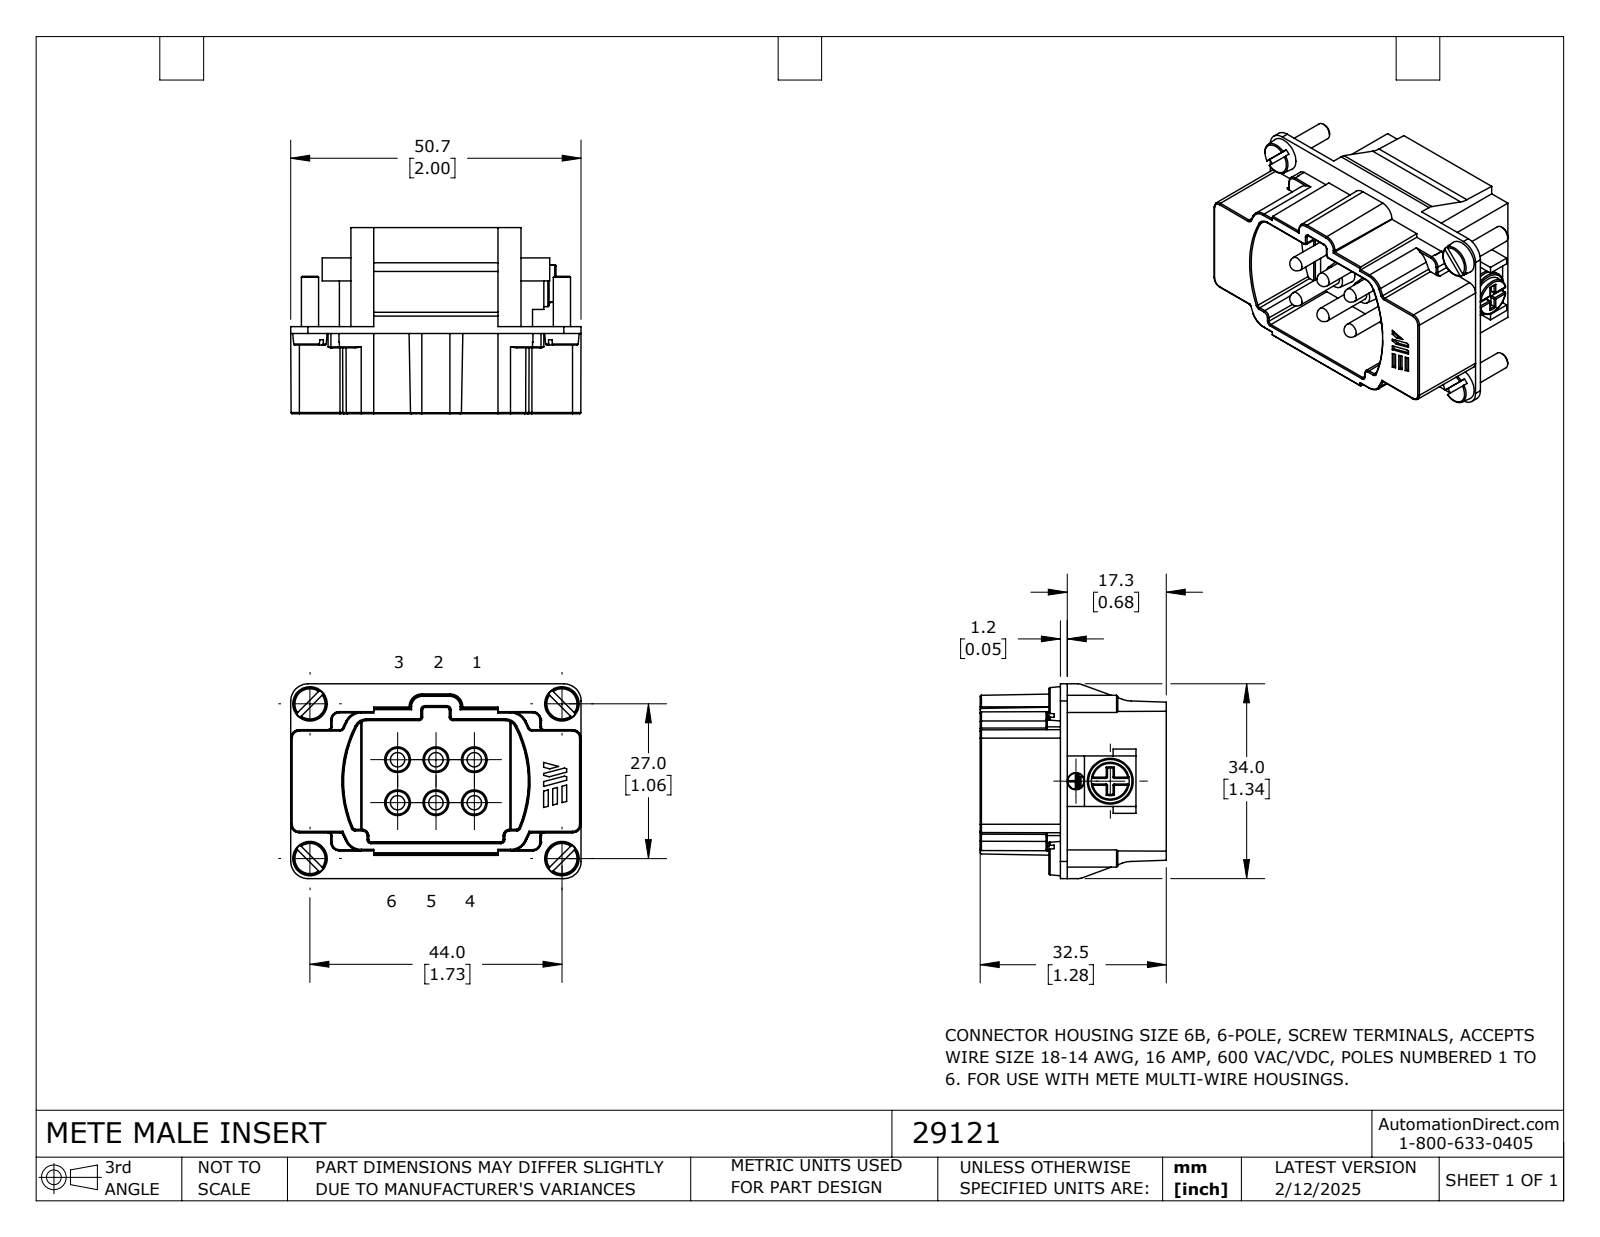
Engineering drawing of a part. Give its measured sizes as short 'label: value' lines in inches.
name: 29121
written by: SolidWorks 2024 (CONFIG_CONTROL_DESIGN)
unit: in
bodies: 1 solid, 426 faces (193 planar, 91 cylindrical, 142 other)
size: 1.996 × 1.339 × 1.28
volume: 1.569 in³; area: 16.32 in²
holes: 1× ⌀0.118
bosses: 6× ⌀0.098, 4× ⌀0.118, 1× ⌀0.315, 1× ⌀0.261, 1× ⌀0.11
rounds: 37× R0.008, 4× R0.118, 2× R0.079, 2× R0.197, 1× R0.091
face distances: 0.047, 0.728, 0.681, 0.598, 1.28, 0.551, 0.157, 1.169, 1.012, 0.079
